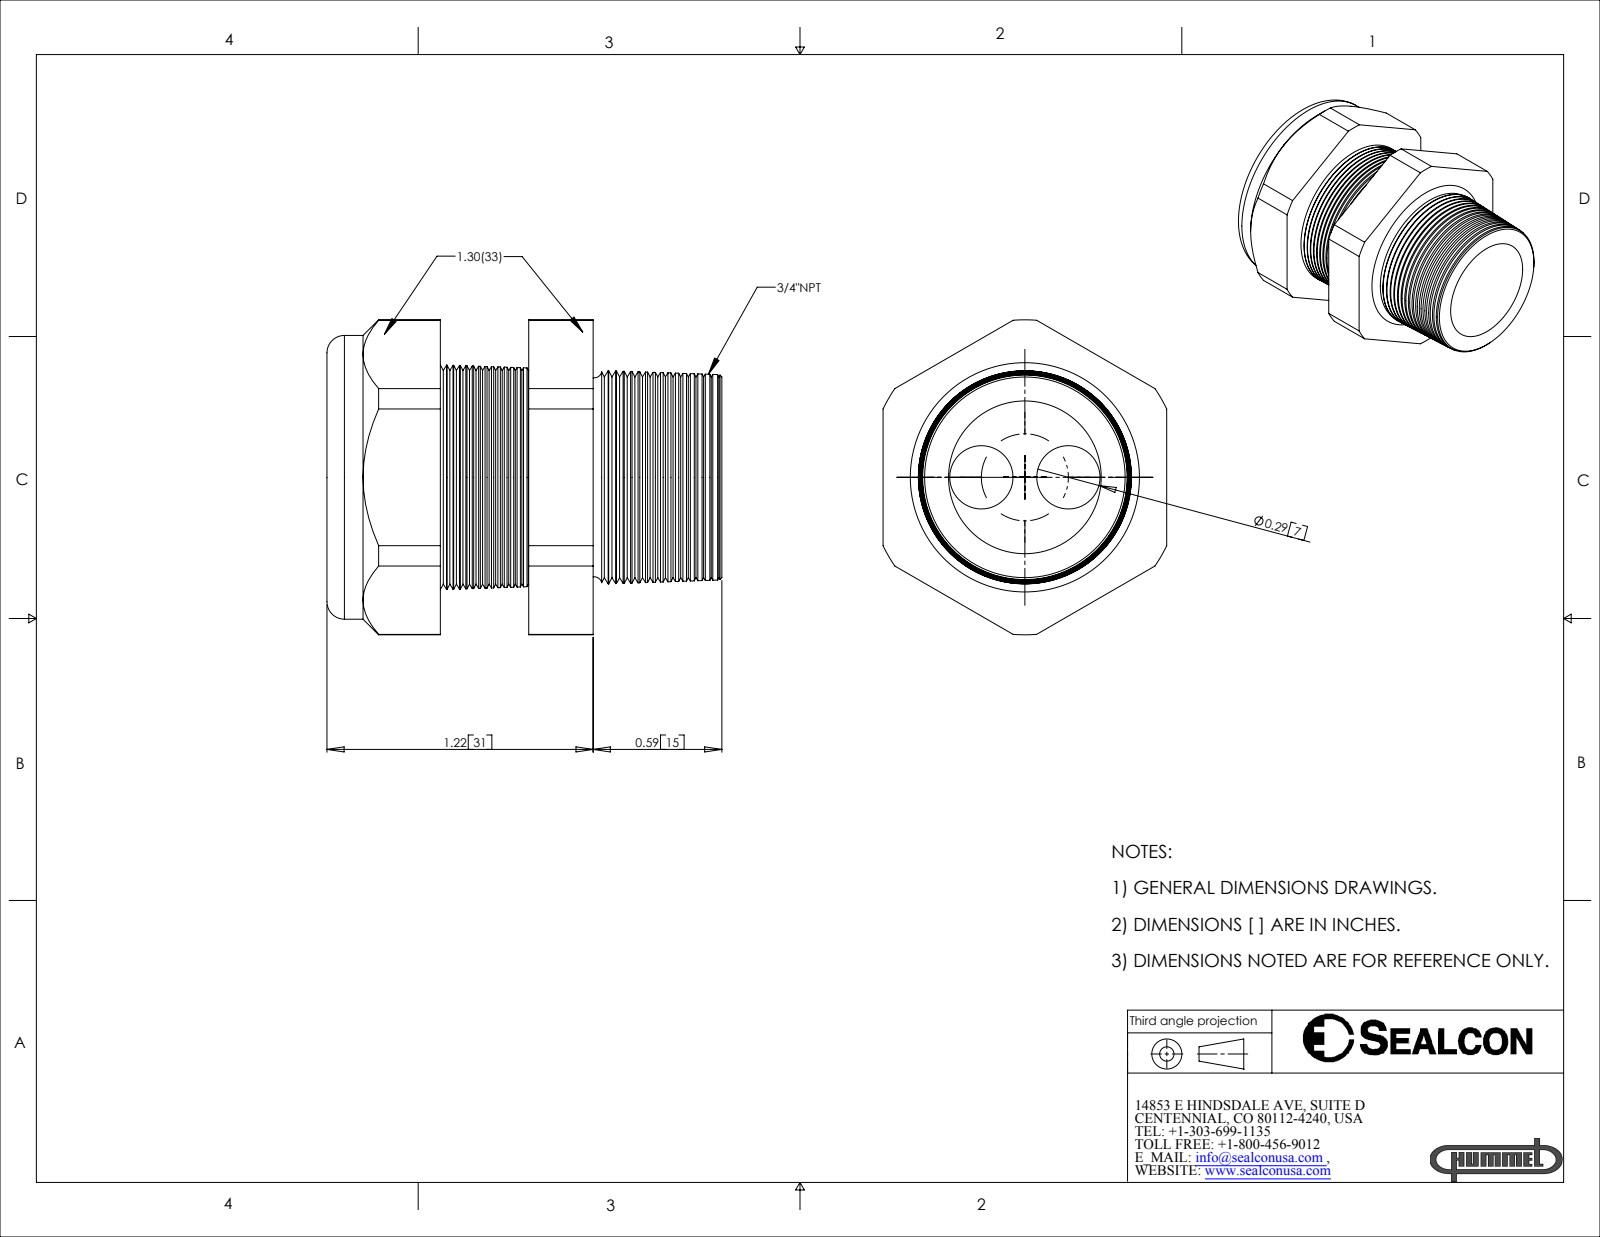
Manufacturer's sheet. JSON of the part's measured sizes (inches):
{"part_name": "CD21N9-GY", "step_written_by": "SolidWorks 2007 (CONFIG_CONTROL_DESIGN)", "units": "inches", "bodies": {"solids": 2, "faces": 232, "planar": 20, "cylindrical": 24, "other": 188}, "overall_size": [1.77, 1.443, 1.3], "volume_in3": 1.246, "surface_area_in2": 17.68, "round_holes": [[0.29, 2], [0.69, 1], [0.71, 1]], "round_bosses_or_shafts": [[1.3, 1]], "partial_cylinders_radius": [[0.721, 1]], "face_to_face_distances": [1.3, 0.925, 0.52, 0.405, 1.22, 0.7, 0.295, 1.77, 1.25, 0.845], "hole_center_spacings": [0.2, 0.399]}
